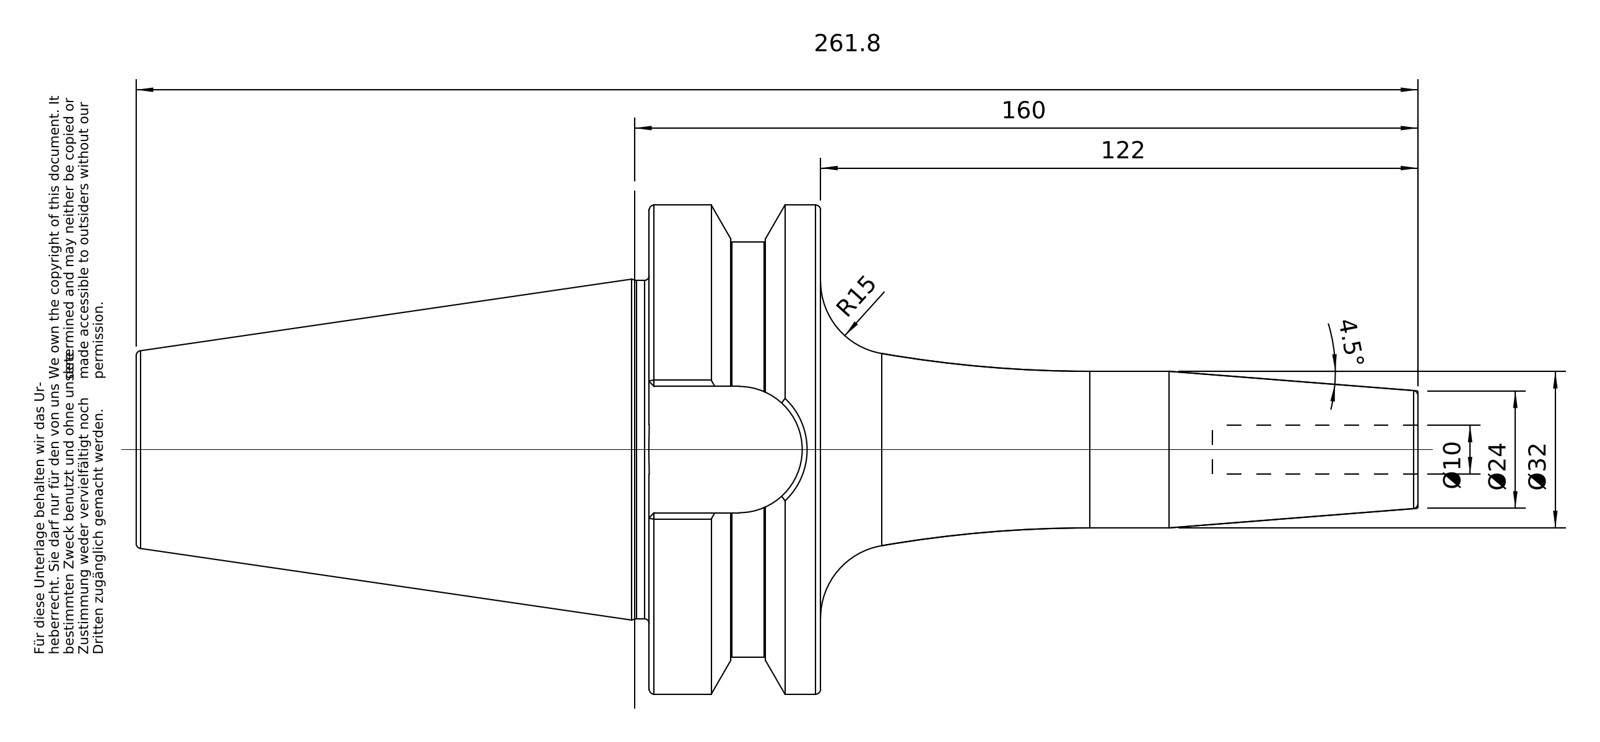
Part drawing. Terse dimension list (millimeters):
name: 50-642-10
written by: PRO/ENGINEER BY PARAMETRIC TECHNOLOGY CORPORATION, 2010430 (CONFIG_CONTROL_DESIGN)
unit: mm
bodies: 1 solid, 98 faces (26 planar, 22 cylindrical, 50 other)
size: 261.8 × 99.97 × 99.97
volume: 570 666 mm³; area: 63 974 mm²
holes: 1× ⌀10, 1× ⌀20.75, 1× ⌀25.02, 1× ⌀25.7
bosses: 1× ⌀99.97, 1× ⌀84.75, 1× ⌀69.15, 1× ⌀32, 1× ⌀24.01
rounds: 1× R12.9
face distances: 35, 70.4, 104.8, 139.8, 25.8, 261.8, 157, 122, 48, 56.8
